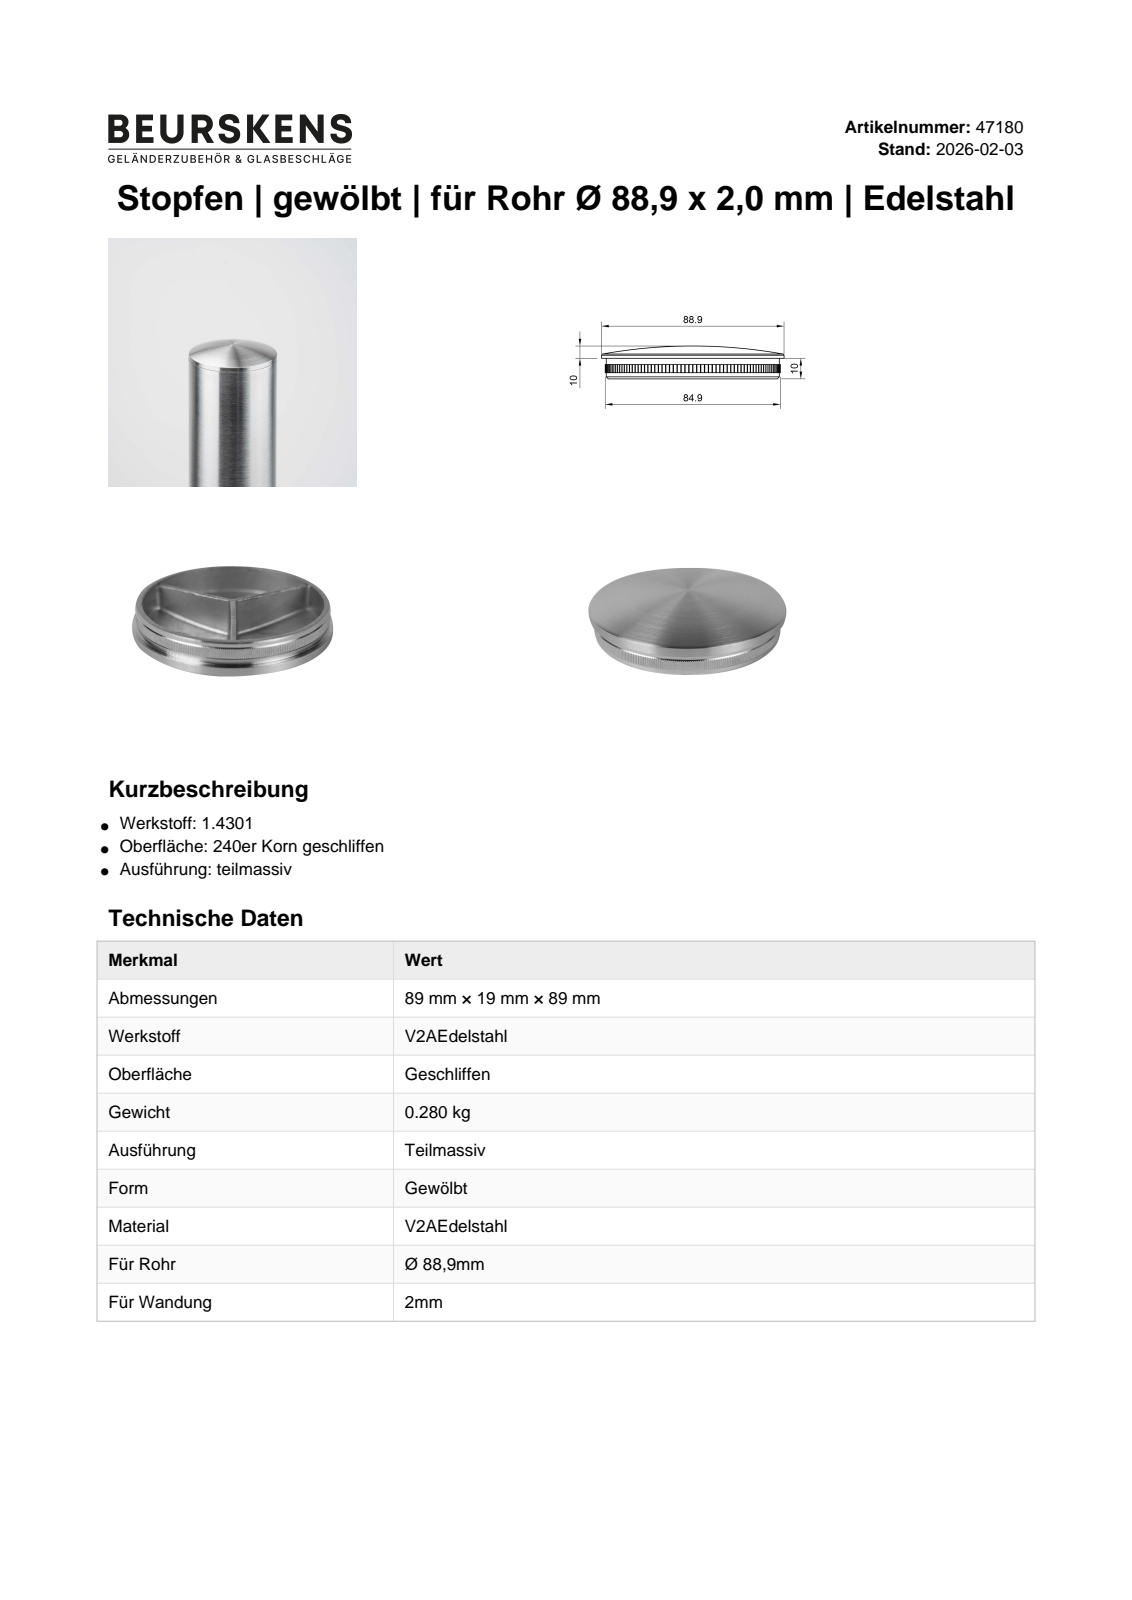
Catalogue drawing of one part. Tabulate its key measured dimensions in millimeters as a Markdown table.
| quantity | value |
| --- | --- |
| part name | 47180 |
| STEP written by | Autodesk Inventor 2022 (AUTOMOTIVE_DESIGN) |
| units | millimeters |
| bodies | 1 solid, 292 faces (5 planar, 284 cylindrical, 3 other) |
| overall size | 88.9 × 88.9 × 16 |
| volume | 40 315 mm³ |
| surface area | 18 064 mm² |
| round holes (diameter × count) | 72 × 1 |
| round bosses / shafts (diameter × count) | 88.9 × 1, 85.3 × 1, 84.3 × 1 |
| partial cylindrical surfaces (radius × count) | 0.12 × 140 |
| main face-to-face distances | 10, 3, 7, 4 |
